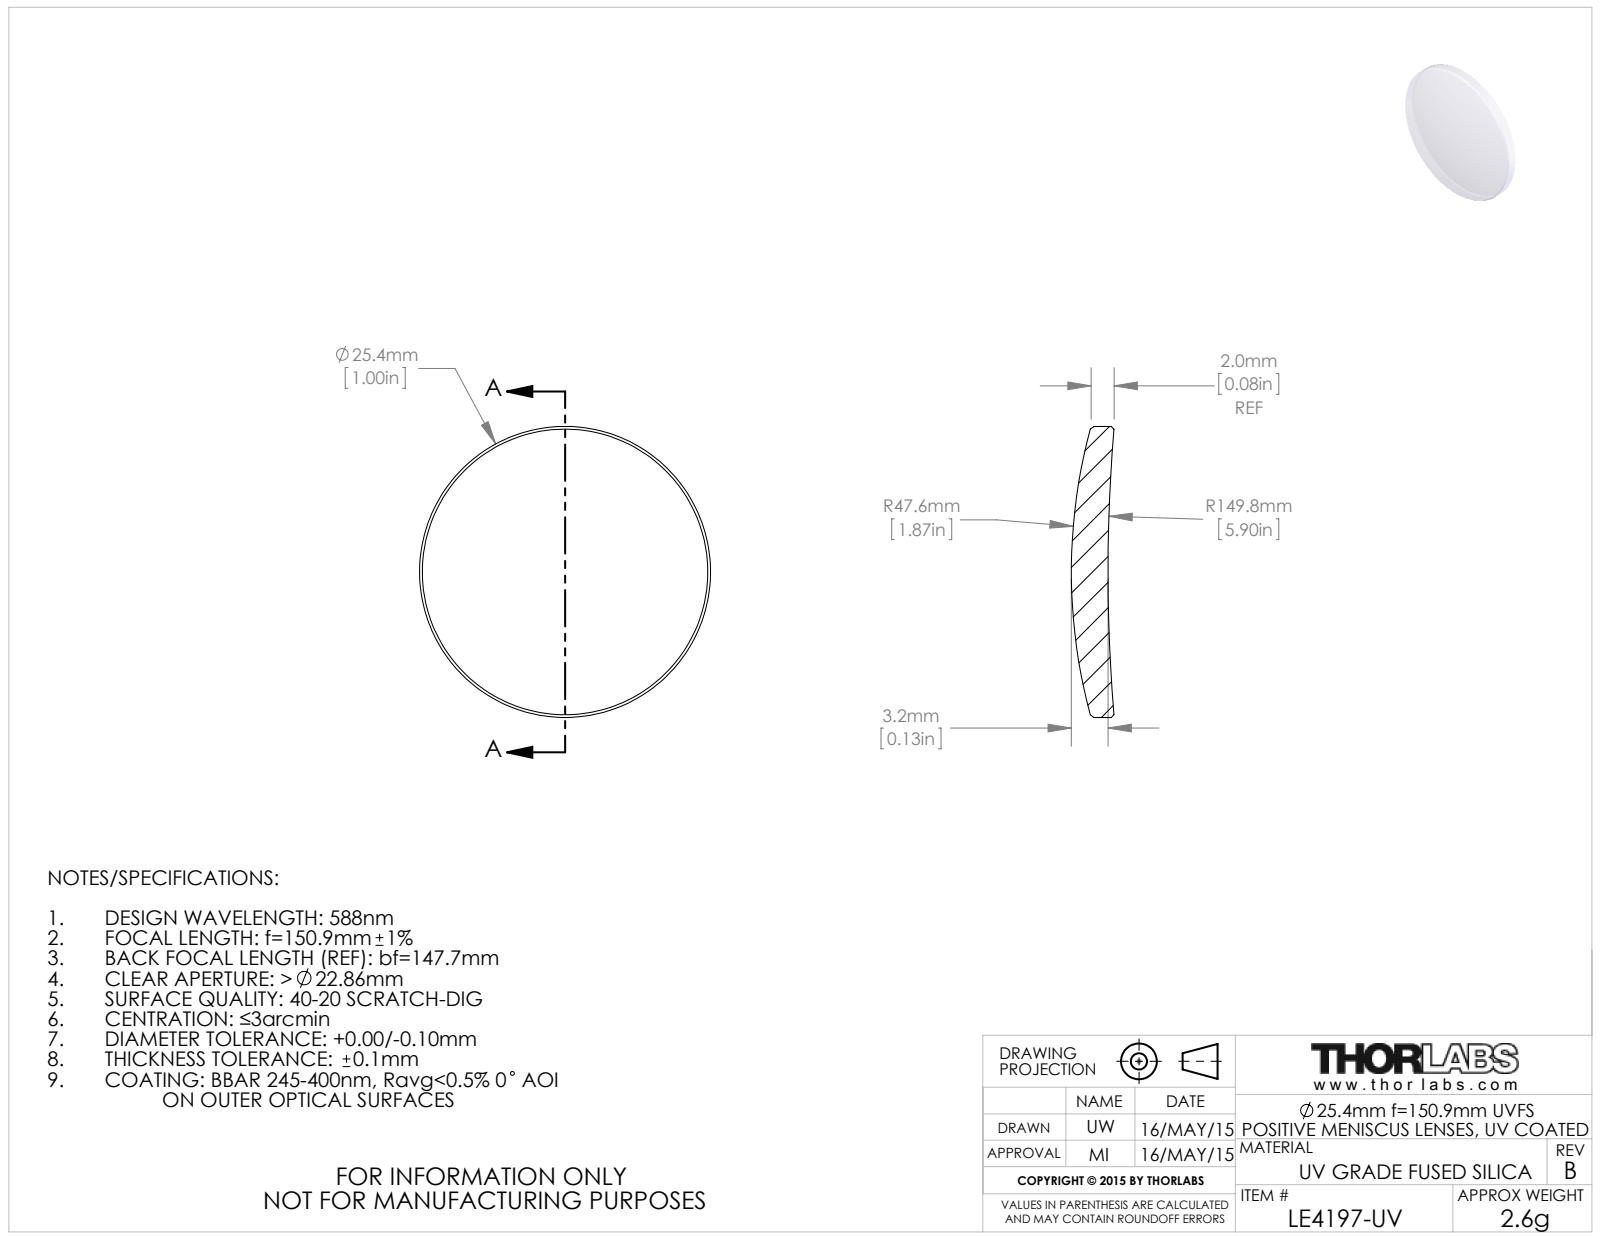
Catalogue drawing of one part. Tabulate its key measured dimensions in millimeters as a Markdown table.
| quantity | value |
| --- | --- |
| part name | 4926-E0W |
| STEP written by | SolidWorks 2014 (CONFIG_CONTROL_DESIGN) |
| units | millimeters |
| bodies | 1 solid, 10 faces (0 planar, 2 cylindrical, 8 other) |
| overall size | 25.4 × 25.4 × 3.72 |
| volume | 1 319 mm³ |
| surface area | 1 163 mm² |
| round bosses / shafts (diameter × count) | 25.4 × 1 |
